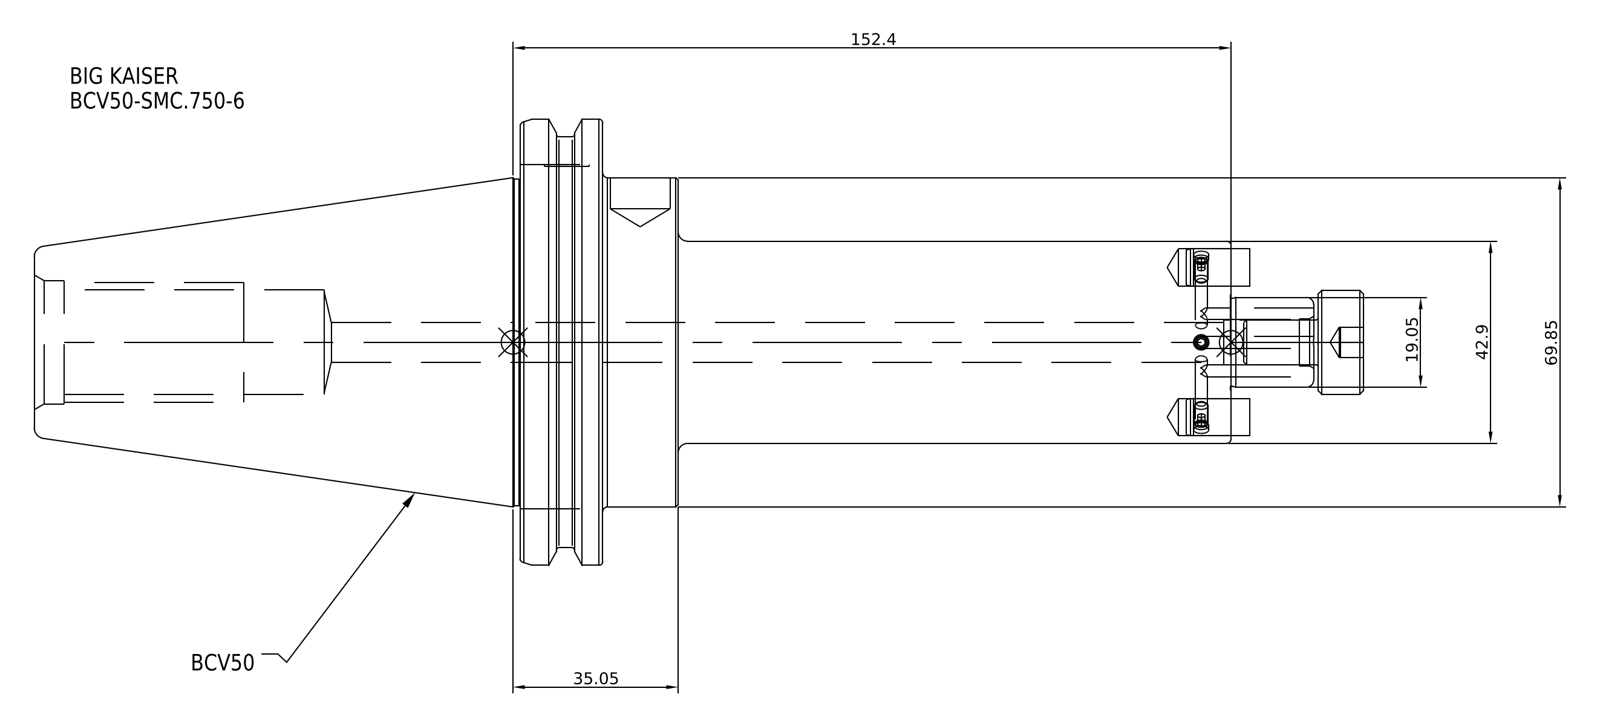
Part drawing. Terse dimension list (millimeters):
name: BCV50-SMC_750-6
written by: SolidWorks 2021 (CONFIG_CONTROL_DESIGN)
unit: mm
bodies: 1 solid, 38 faces (18 planar, 14 cylindrical, 6 other)
size: 257.96 × 98.43 × 98.43
volume: 606 250 mm³; area: 60 159 mm²
holes: 1× ⌀8.43
bosses: 1× ⌀98.43, 1× ⌀91.29, 1× ⌀69.85, 1× ⌀42.9
face distances: 17.55, 16, 33.55, 136.65, 120.65, 103.1, 117.35, 133.35, 150.9, 254
